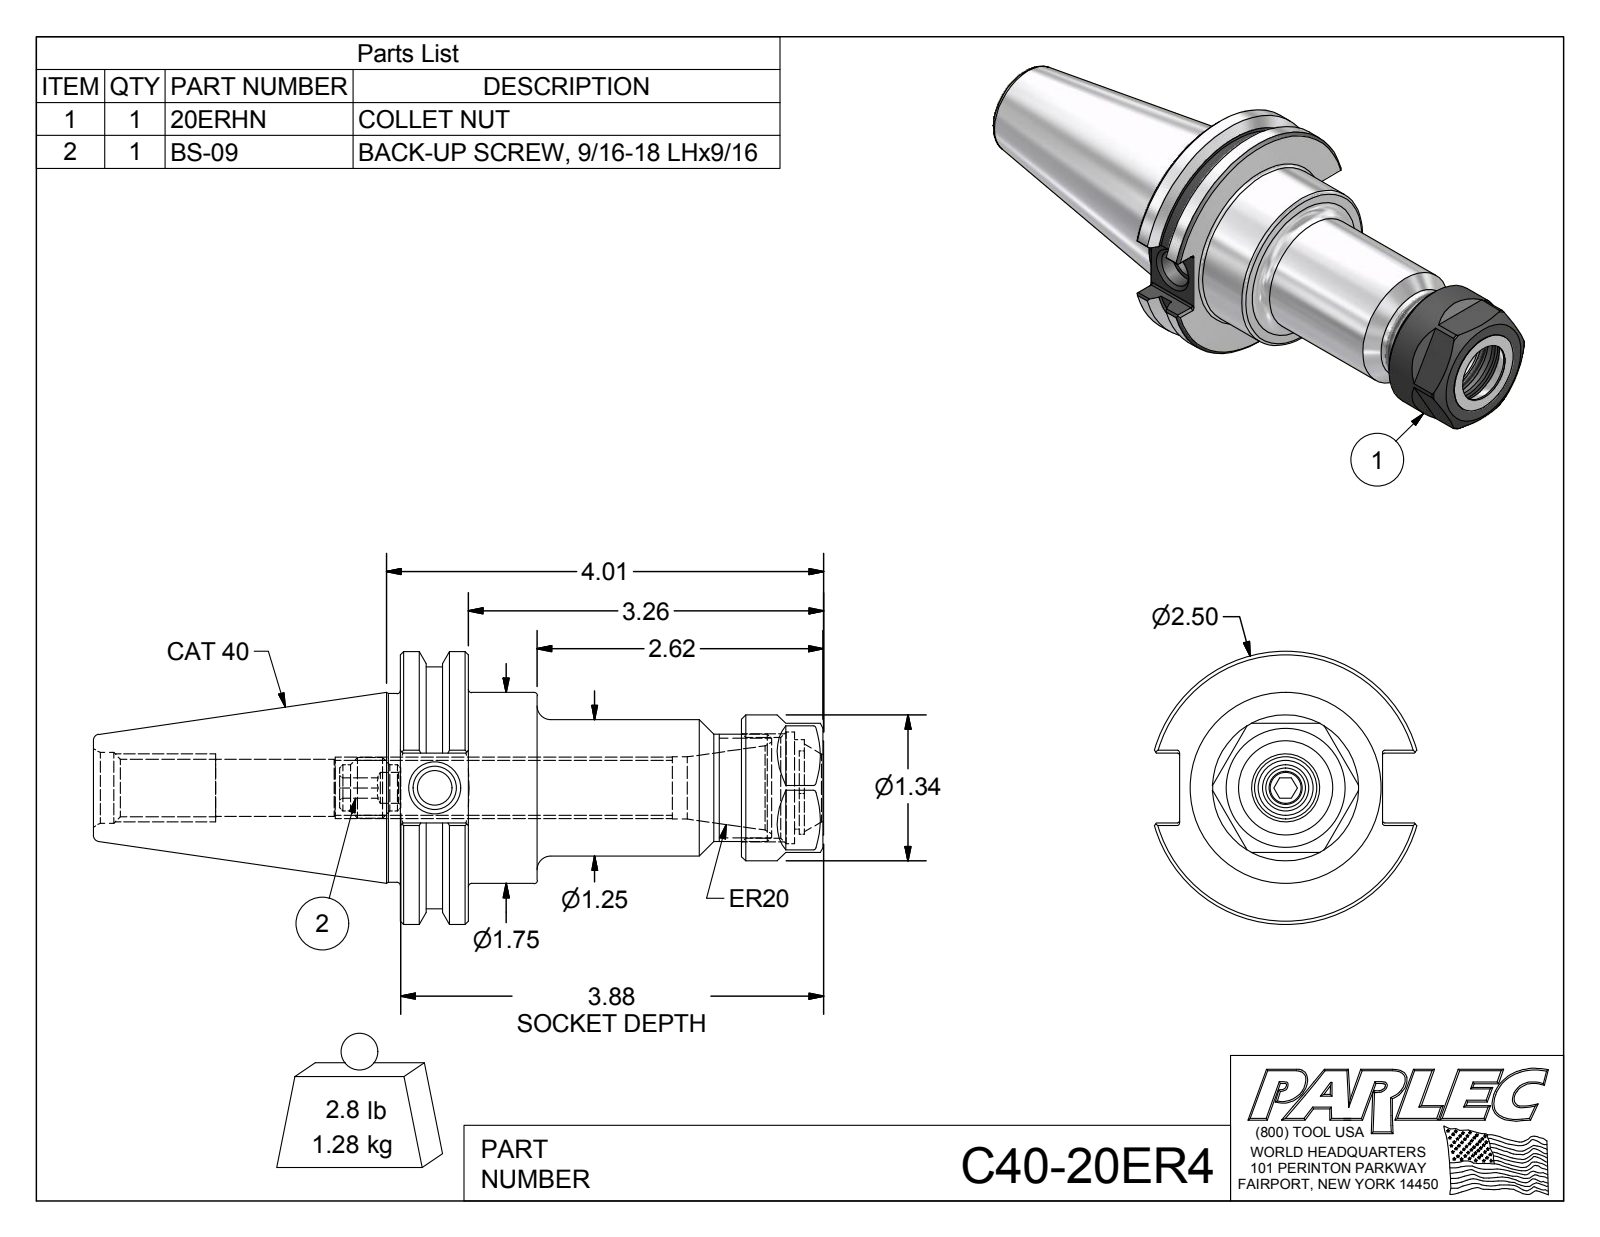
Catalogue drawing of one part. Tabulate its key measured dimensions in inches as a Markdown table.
| quantity | value |
| --- | --- |
| part name | C40-20ER4; C40-20ER4-1; 20ERHN; BS-09 |
| STEP written by | Autodesk Inventor 2012 (AUTOMOTIVE_DESIGN) |
| units | inches |
| bodies | 3 solids, 147 faces (65 planar, 40 cylindrical, 42 other) |
| overall size | 6.693 × 2.5 × 2.403 |
| volume | 9.936 in³ |
| surface area | 55.17 in² |
| round holes (diameter × count) | 0.281 × 1, 0.315 × 1, 0.399 × 1, 0.502 × 1, 0.525 × 1, 0.527 × 1, 0.57 × 1, 0.62 × 1, 0.648 × 1, 0.82 × 1, 0.925 × 1, 1.024 × 1 |
| round bosses / shafts (diameter × count) | 2.5 × 1, 2.219 × 1, 1.75 × 1, 1.73 × 1, 1.339 × 1, 1.25 × 1, 0.984 × 1, 0.86 × 1 |
| partial cylindrical surfaces (radius × count) | 0.02 × 12, 0.423 × 1 |
| main face-to-face distances | 0.625, 1.181, 1.255, 0.63, 3.127, 2.502, 1.872, 0.27, 0.911, 3.875 |
| hole center spacings | 0.037 |
